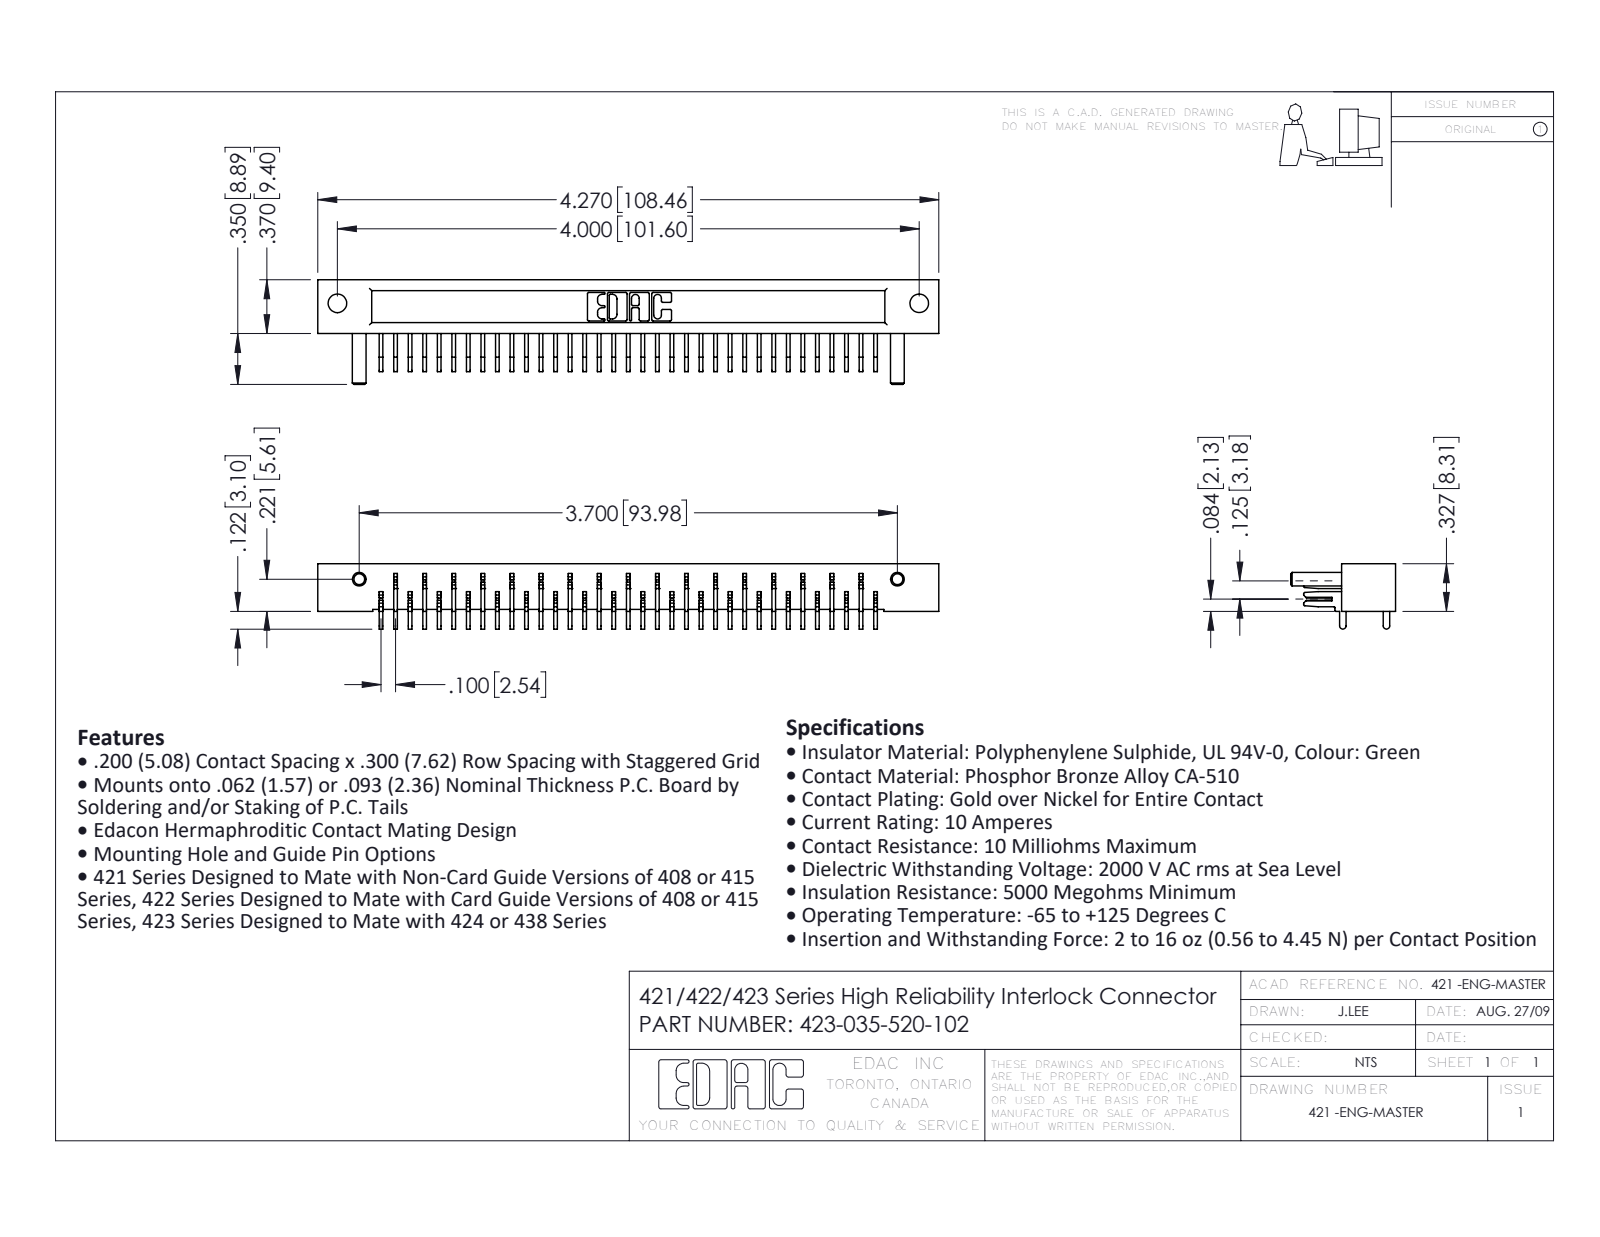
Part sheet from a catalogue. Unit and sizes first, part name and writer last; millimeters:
Units: millimetres
Overall size (bounding box): 108.5 × 18.3 × 11.4
Round holes (diameter × count): ⌀3.3 ×2
Round bosses / shafts (diameter × count): ⌀2.4 ×2
Partial cylindrical surfaces — rounded edges, fillets, slot ends (radius × count): R0.3 ×22, R0.2 ×6, R0.8 ×6, R0.2 ×4, R0.3 ×4, R0.4 ×4, R0.7 ×3, R0.6 ×2
Main face-to-face distances: 5.1, 10.2, 15.2, 20.3, 25.4, 30.5, 35.6, 40.6, 45.7, 50.8
Hole centre spacings: 101.6
Volume: 8 310 mm³ · Surface area: 12 420 mm²
Bodies: 36 solids, 1201 faces (971 planar, 226 cylindrical, 4 other)
Part name (STEP PRODUCT): 423 Part_35; 421-290-001_120; 421-290-002_120; 423-035-520-102
STEP written by: SolidWorks 2016 (CONFIG_CONTROL_DESIGN)
